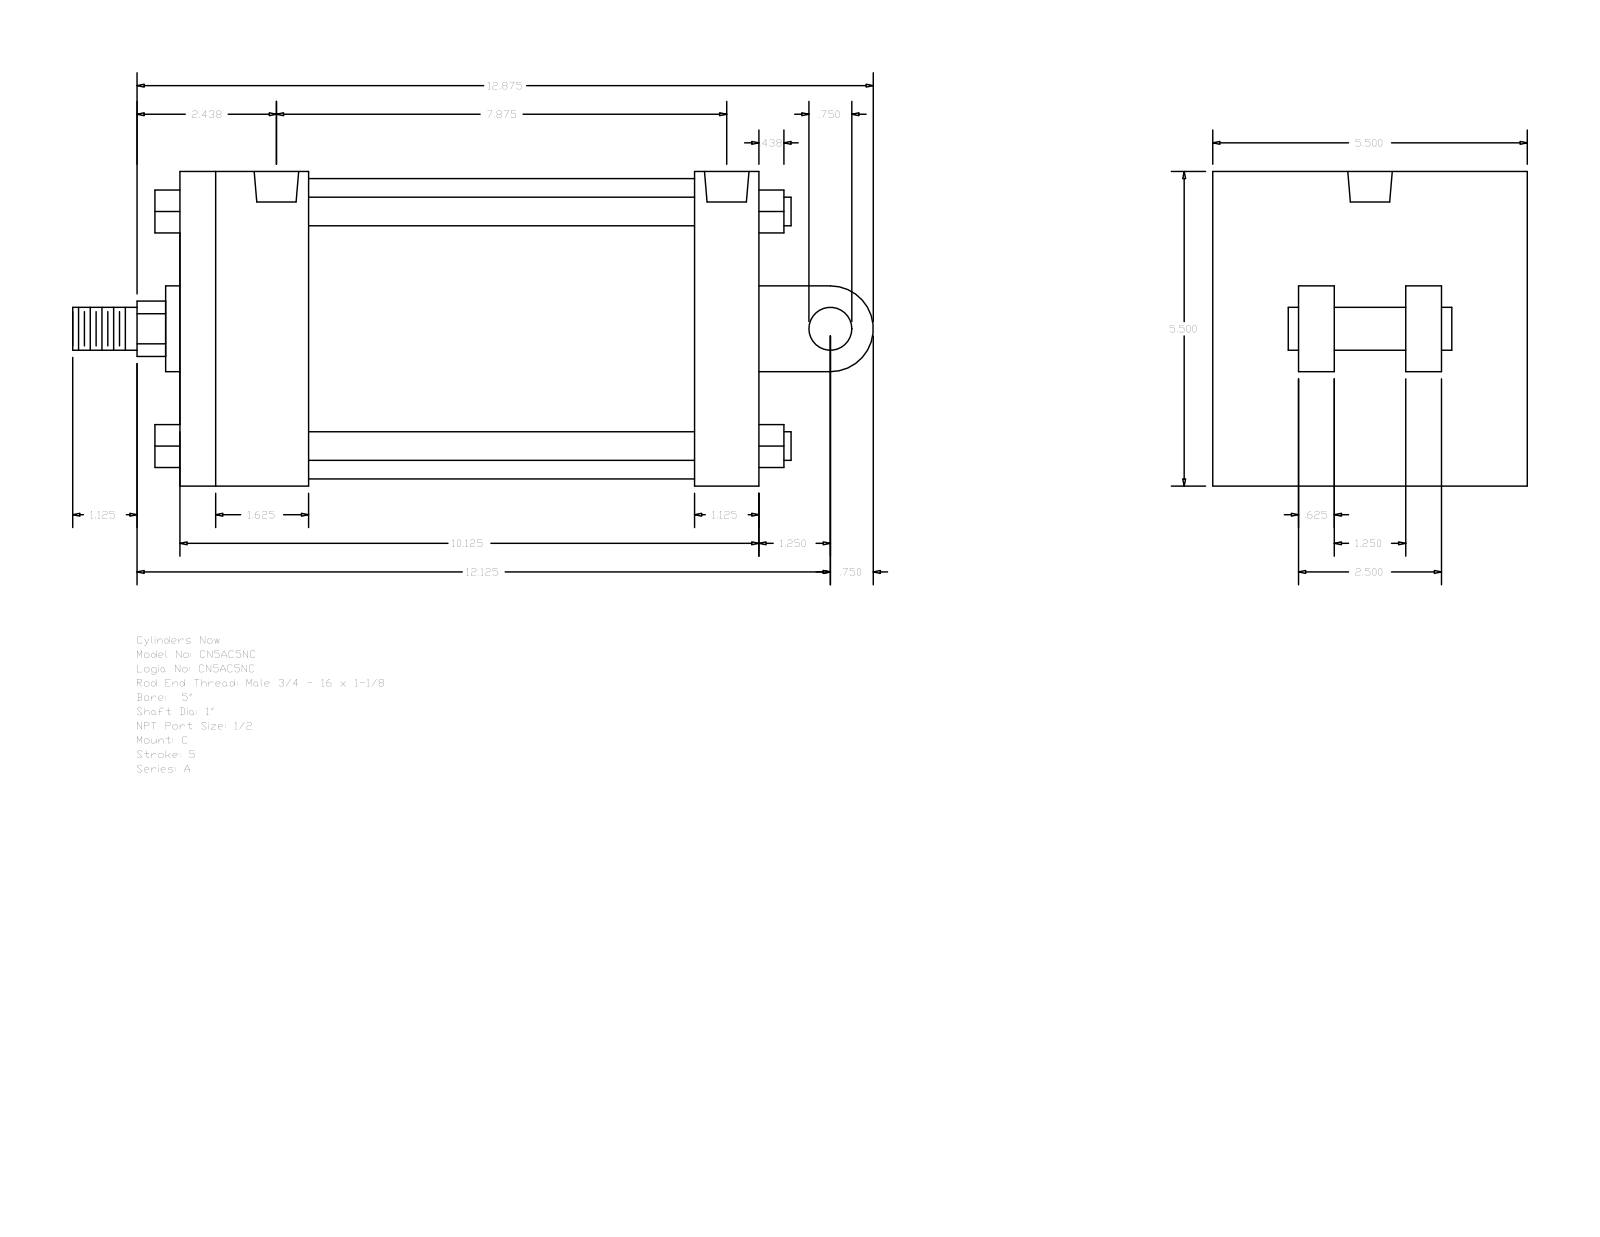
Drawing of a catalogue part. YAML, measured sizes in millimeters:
part_name: "A_C__0500_1"
step_written_by: "GSSL Pune (CONFIG_CONTROL_DESIGN)"
units: millimeters
bodies: {solids: 0, faces: 135, planar: 102, cylindrical: 33, other: 0}
overall_size: [355.6, 139.7, 139.7]
round_holes:
  - {diameter: 8.73, count: 4}
  - {diameter: 19.77, count: 2}
round_bosses_or_shafts:
  - {diameter: 12.7, count: 4}
  - {diameter: 19.05, count: 2}
  - {diameter: 133.35, count: 1}
  - {diameter: 38.1, count: 1}
  - {diameter: 25.4, count: 1}
partial_cylinders:
  - {radius: 12.29, count: 1}
  - {radius: 19.05, count: 1}
face_to_face_distances: [139.7, 257.18, 57.15, 228.6, 171.45, 200.03, 28.58, 38.1, 101.6, 53.97]
hole_center_spacings: [2.39, 195.25, 197.64, 200.03]
